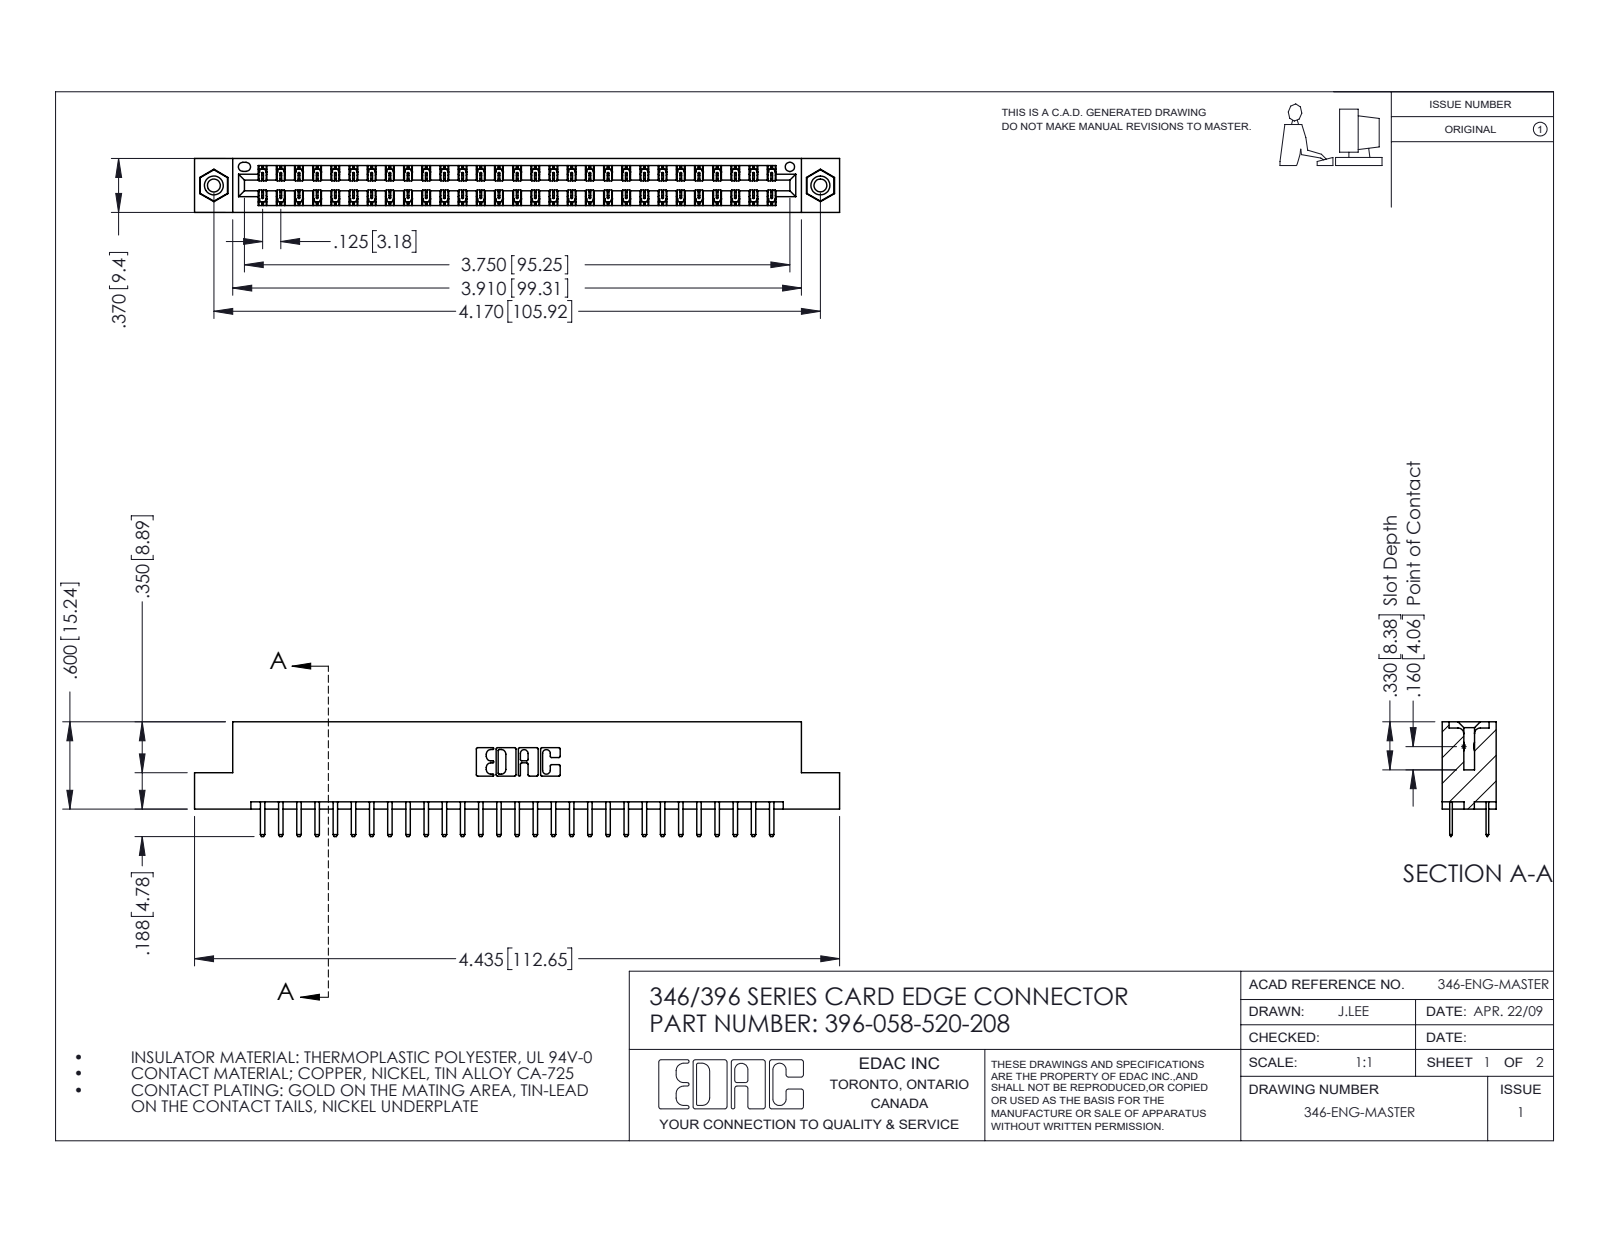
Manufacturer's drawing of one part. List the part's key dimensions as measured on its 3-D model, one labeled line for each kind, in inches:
Part name (STEP PRODUCT): 396-058-520-208; 345-292-001_345-293-120; 346 Part_Flush Mounting Lugs - 0.156 Dia-TI; 345-250-001_345-250-003-102
STEP written by: SolidWorks 2016 (CONFIG_CONTROL_DESIGN)
Units: inches
Bodies: 61 solids, 3430 faces (2254 planar, 1160 cylindrical, 16 other)
Overall size (bounding box): 4.435 × 0.788 × 0.37
Volume: 0.662 in³ · Surface area: 22.74 in²
Round holes (diameter × count): ⌀0.089 ×2, ⌀0.125 ×2, ⌀0.156 ×2, ⌀0.064 ×1
Round bosses / shafts (diameter × count): ⌀0.155 ×2
Partial cylindrical surfaces — rounded edges, fillets, slot ends (radius × count): R0.006 ×87, R0.01 ×62, R0.01 ×22, R0.007 ×6, R0.031 ×6, R0.026 ×3, R0.014 ×2, R0.022 ×2
Main face-to-face distances: 0.048, 0.322, 0.25, 0.37, 0.275, 0.072, 0.298, 0.025, 0.148, 0.222
Hole centre spacings: 0.246, 3.962, 4.17
